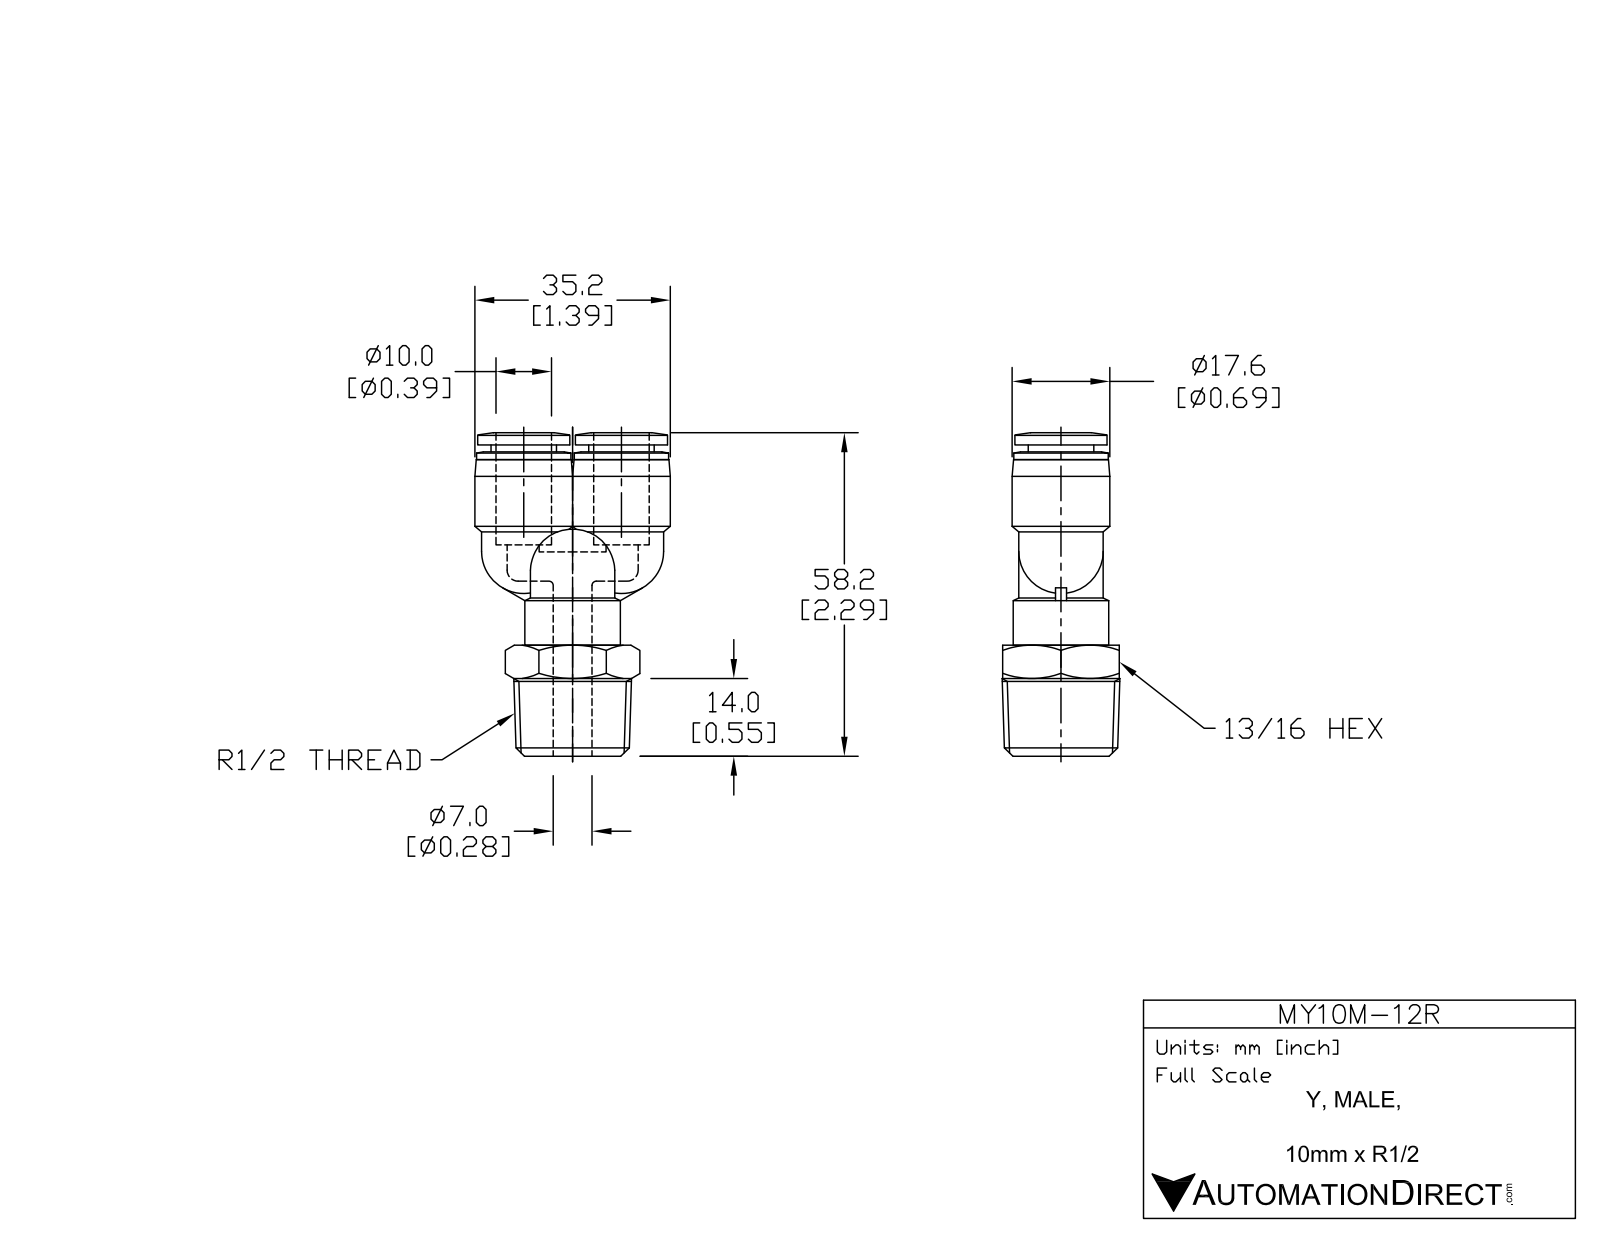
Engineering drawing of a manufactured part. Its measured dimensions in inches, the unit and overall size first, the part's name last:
Units: inches
Overall size (bounding box): 2.293 × 1.386 × 0.827
Round holes (diameter × count): ⌀0.315 ×4, ⌀0.406 ×2
Round bosses / shafts (diameter × count): ⌀0.598 ×3, ⌀0.693 ×2, ⌀0.669 ×2, ⌀0.654 ×2, ⌀0.465 ×2, ⌀0.677 ×1
Main face-to-face distances: 0.827, 2.207, 2.157, 0.049, 0.787, 1.37, 1.419, 1.494, 0.707, 0.663
Hole centre spacings: 0.346, 0.693
Volume: 0.997 in³ · Surface area: 13.65 in²
Bodies: 1 solid, 109 faces (23 planar, 35 cylindrical, 51 other)
Part name (STEP PRODUCT): MY10M-12R
STEP written by: SolidWorks 2015 (AUTOMOTIVE_DESIGN)
